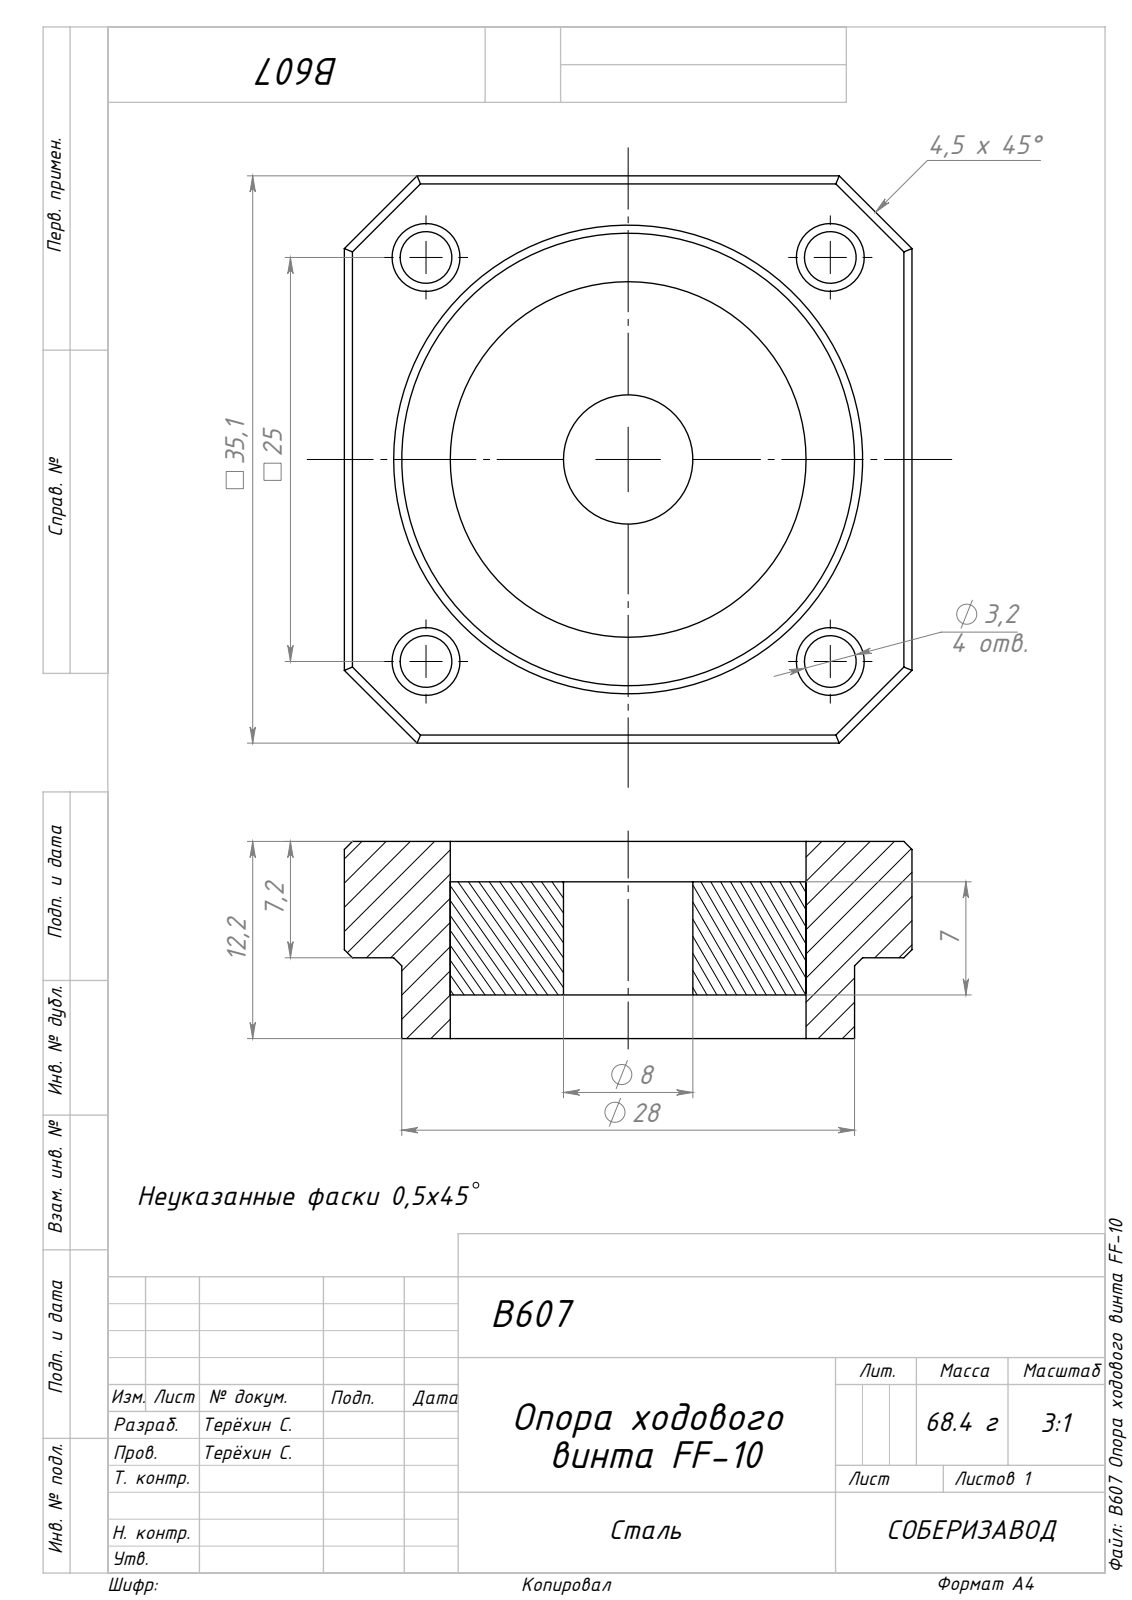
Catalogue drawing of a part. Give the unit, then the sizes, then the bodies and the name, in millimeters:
Units: millimetres
Overall size (bounding box): 35.1 × 35.1 × 12.2
Round holes (diameter × count): ⌀3.2 ×4, ⌀6.5 ×4, ⌀8 ×1, ⌀22 ×1
Round bosses / shafts (diameter × count): ⌀28 ×1
Main face-to-face distances: 7.2, 2.5, 9.5, 4.7, 7, 2.3, 35.1, 12.2, 9.7, 5
Hole centre spacings: 17.68, 25, 35.36
Volume: 8 807 mm³ · Surface area: 5 331 mm²
Bodies: 2 solids, 71 faces (29 planar, 24 cylindrical, 18 other)
Part name (STEP PRODUCT): B607 Опора ходового винта FF-10_00; Сборка3
STEP written by: SolidWorks 2024 (AUTOMOTIVE_DESIGN)
